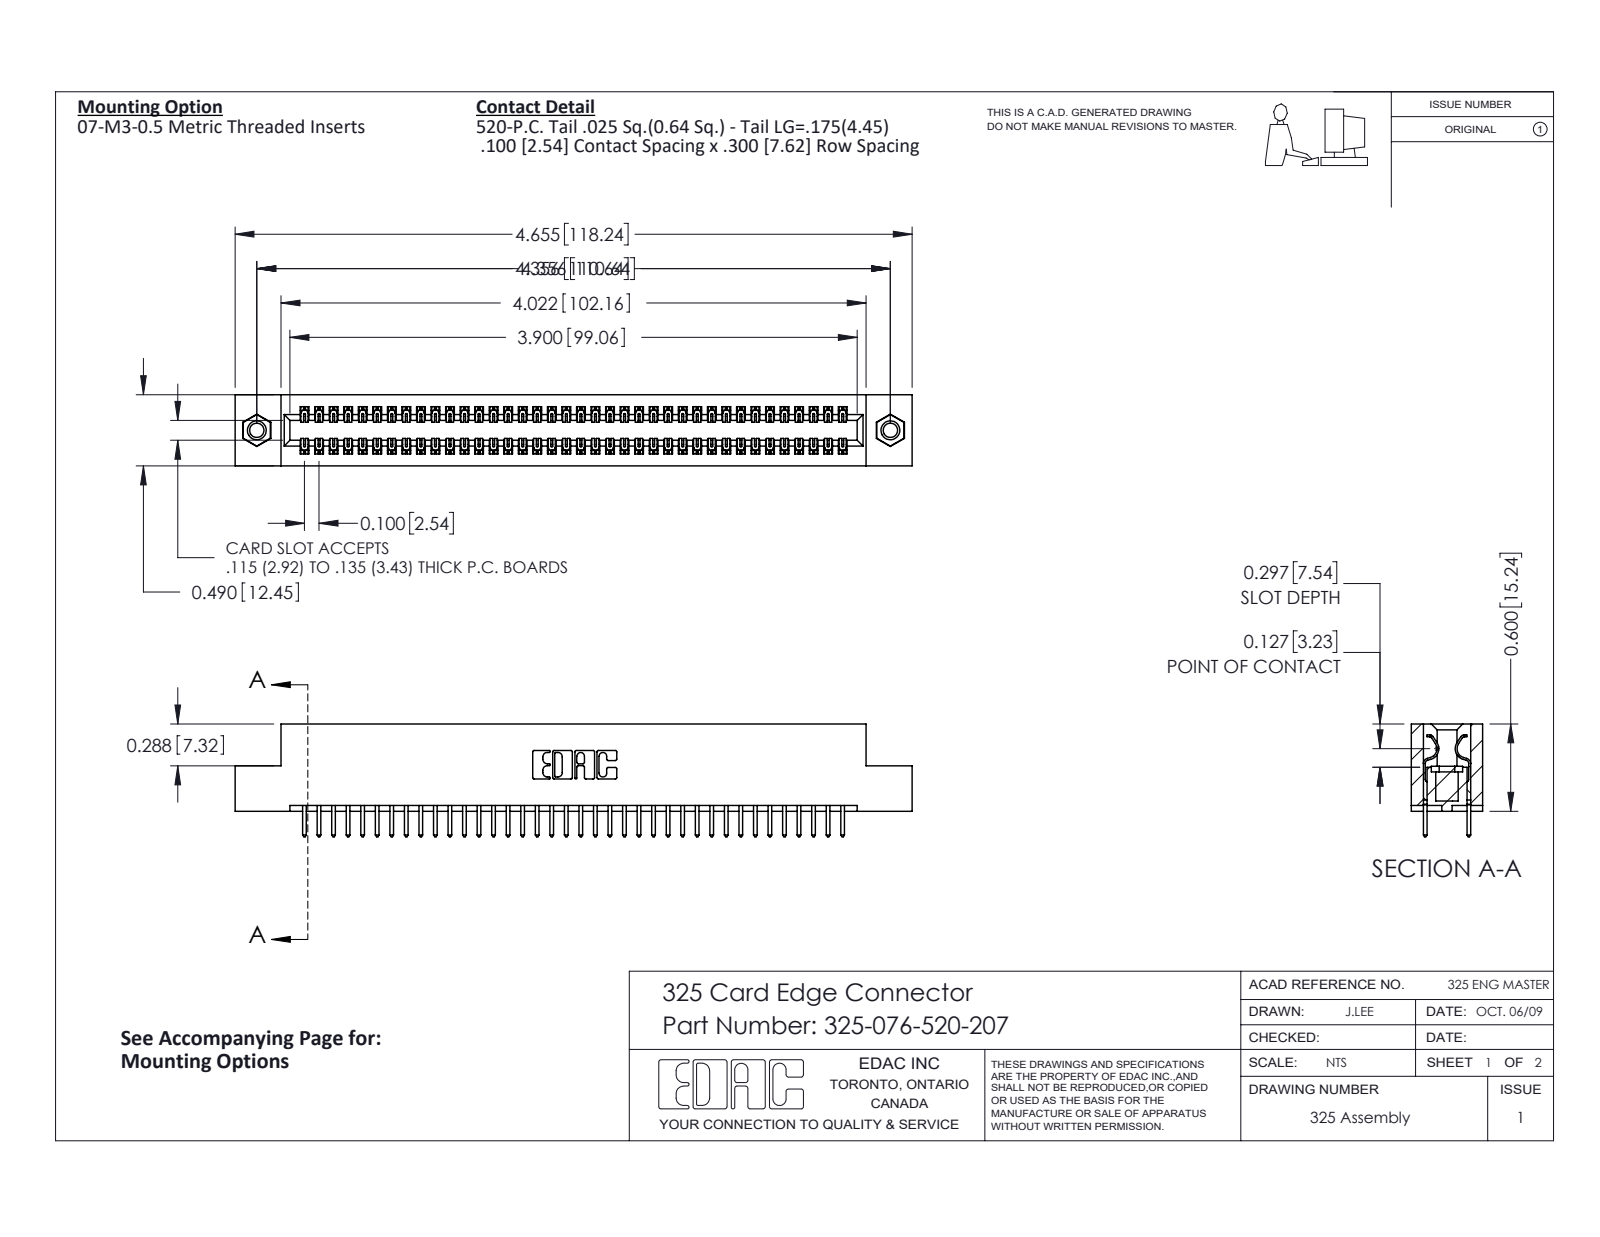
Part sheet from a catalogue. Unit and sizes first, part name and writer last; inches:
Units: inches
Overall size (bounding box): 4.655 × 0.775 × 0.49
Round holes (diameter × count): ⌀0.098 ×2, ⌀0.125 ×2, ⌀0.16 ×2
Round bosses / shafts (diameter × count): ⌀0.155 ×2
Partial cylindrical surfaces — rounded edges, fillets, slot ends (radius × count): R0.006 ×114, R0.01 ×76, R0.01 ×22, R0.007 ×6, R0.031 ×6, R0.026 ×3, R0.014 ×2, R0.022 ×2
Main face-to-face distances: 0.083, 0.407, 0.49, 0.3, 0.107, 0.383, 0.025, 0.325, 0.275, 0.56
Hole centre spacings: 4.356
Volume: 0.928 in³ · Surface area: 28.18 in²
Bodies: 79 solids, 4126 faces (2838 planar, 1272 cylindrical, 16 other)
Part name (STEP PRODUCT): 325-076-520-207; 325-292-001_325-293-120; 325 Part_TI; 345-250-001_345-250-005-103
STEP written by: SolidWorks 2016 (CONFIG_CONTROL_DESIGN)
